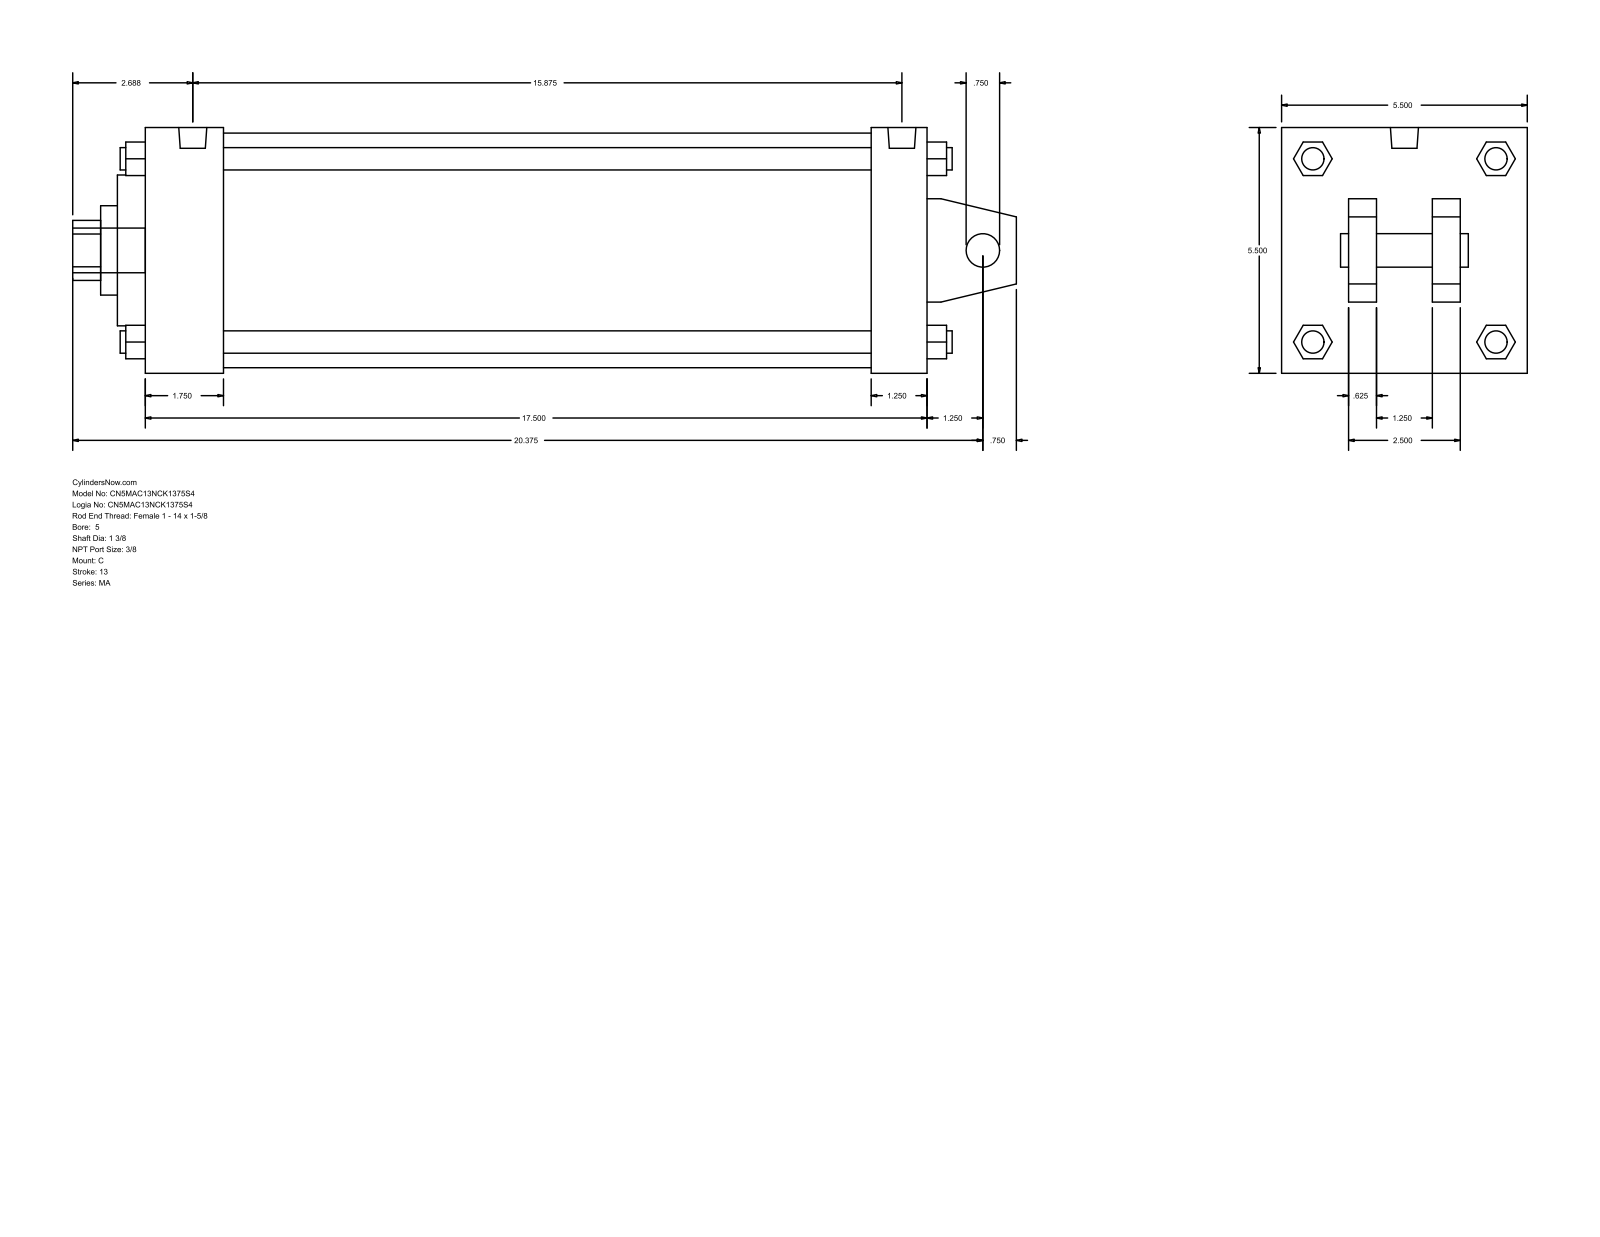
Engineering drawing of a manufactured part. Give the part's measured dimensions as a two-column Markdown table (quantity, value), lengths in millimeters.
| quantity | value |
| --- | --- |
| part name | MA_C__0500_1.375 |
| STEP written by | GSSL Pune (CONFIG_CONTROL_DESIGN) |
| units | millimeters |
| bodies | 0 solids, 141 faces (109 planar, 32 cylindrical, 0 other) |
| overall size | 536.58 × 139.7 × 139.7 |
| round holes (diameter × count) | 19.05 × 1, 34.92 × 1, 50.8 × 1, 85.72 × 1, 133.35 × 1 |
| round bosses / shafts (diameter × count) | 12.7 × 4, 11.11 × 4, 15.93 × 2, 25.4 × 1 |
| partial cylindrical surfaces (radius × count) | 17.06 × 1 |
| main face-to-face distances | 139.7, 444.5, 15.87, 412.75, 31.75, 44.45, 368.3, 400.05, 38.1, 101.6 |
